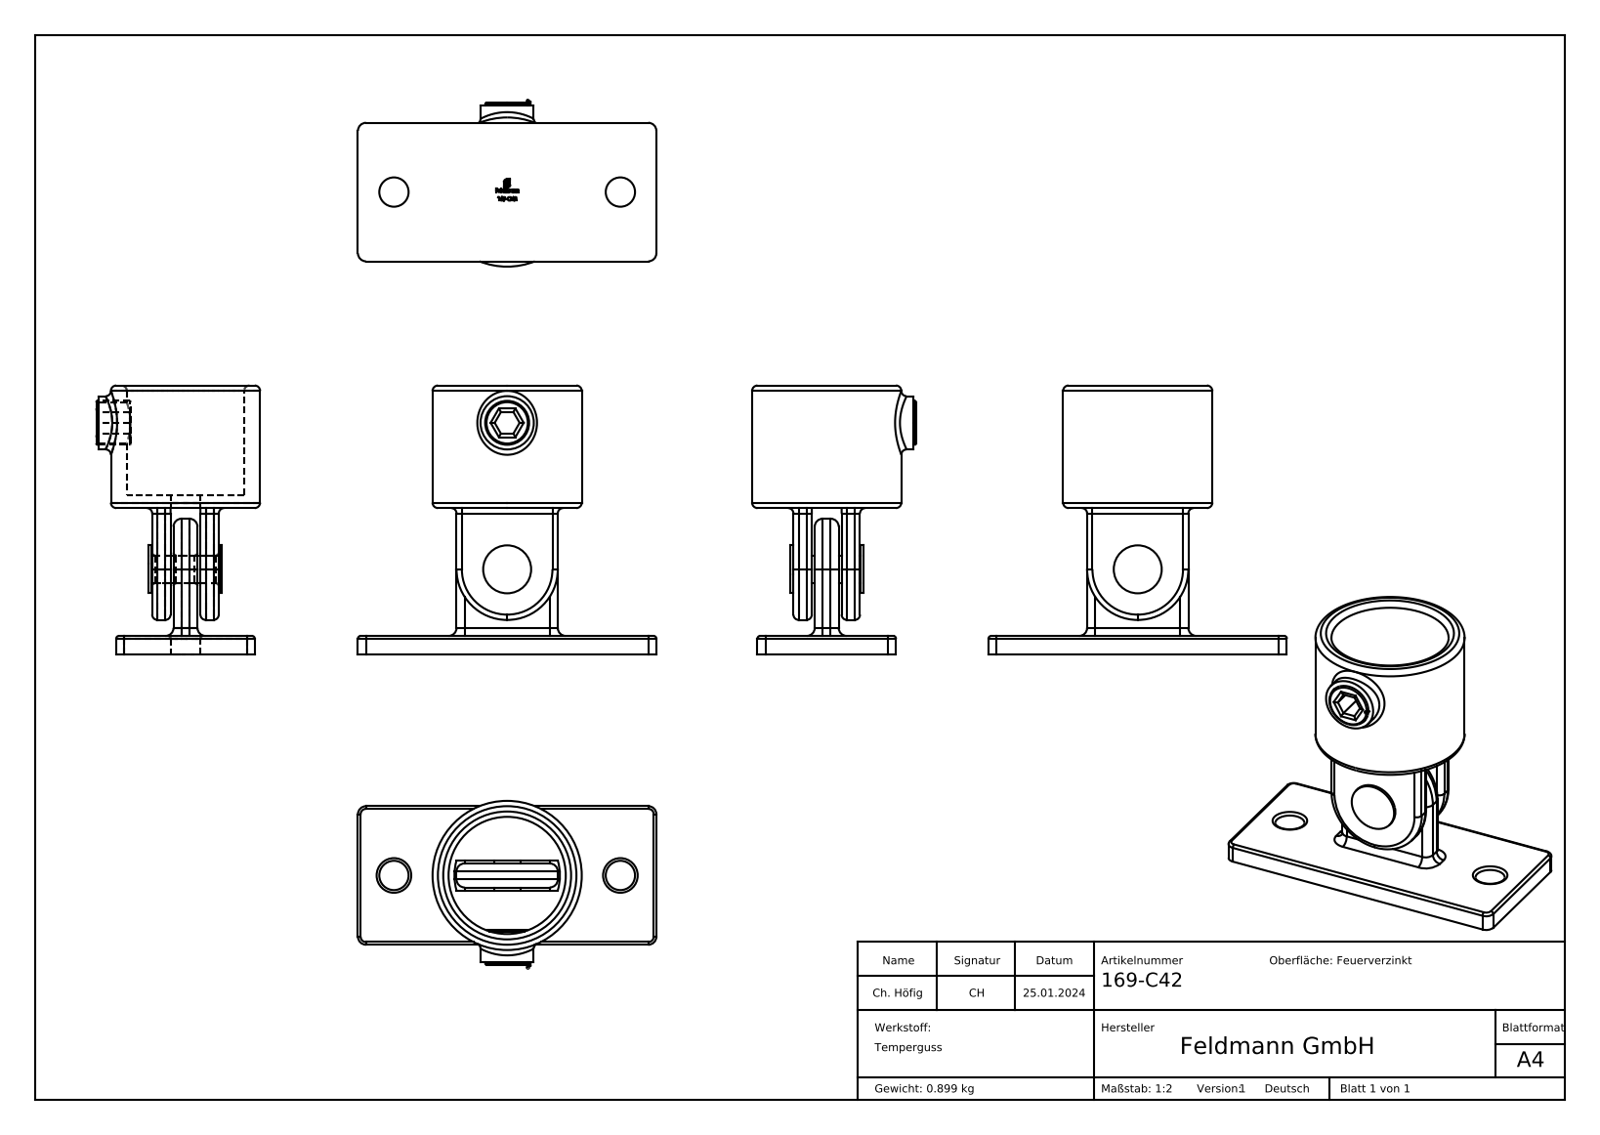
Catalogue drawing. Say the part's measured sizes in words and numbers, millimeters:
The part is named "169-C42; 169-C42 Teil3_169-C42 Teil3; 169-C42 Teil4_169-C42 Teil4; 169-C42 Teil2_169-C42 Teil2 (+1 more)". Its 3-D file was written by "SolidWorks 2018 (CONFIG_CONTROL_DESIGN)". It is 4 solids with 372 faces: 169 planar, 62 cylindrical and 141 other. Overall it measures 112 by 101 by 61.5 millimeters. Its volume is 122 806 cubic millimeters and its surface area 44 984 square millimeters. Round holes: 2 of diameter 11, 1 of diameter 10.5, 1 of diameter 15.25, 1 of diameter 44. Round bosses or shafts: 1 of diameter 56, 1 of diameter 38, 1 of diameter 20, 1 of diameter 18, 1 of diameter 16.5, 1 of diameter 10. Partial cylindrical surfaces (rounded edges, fillets, slot ends): 24 of radius 2, 12 of radius 3, 4 of radius 1, 1 of radius 19.81. The main face-to-face distances are 7, 6.9, 18.1, 8, 17, 1.1, 10.1, 11.2, 13.5, 20.4. The hole center spacings are 42.5, 55, 85.
